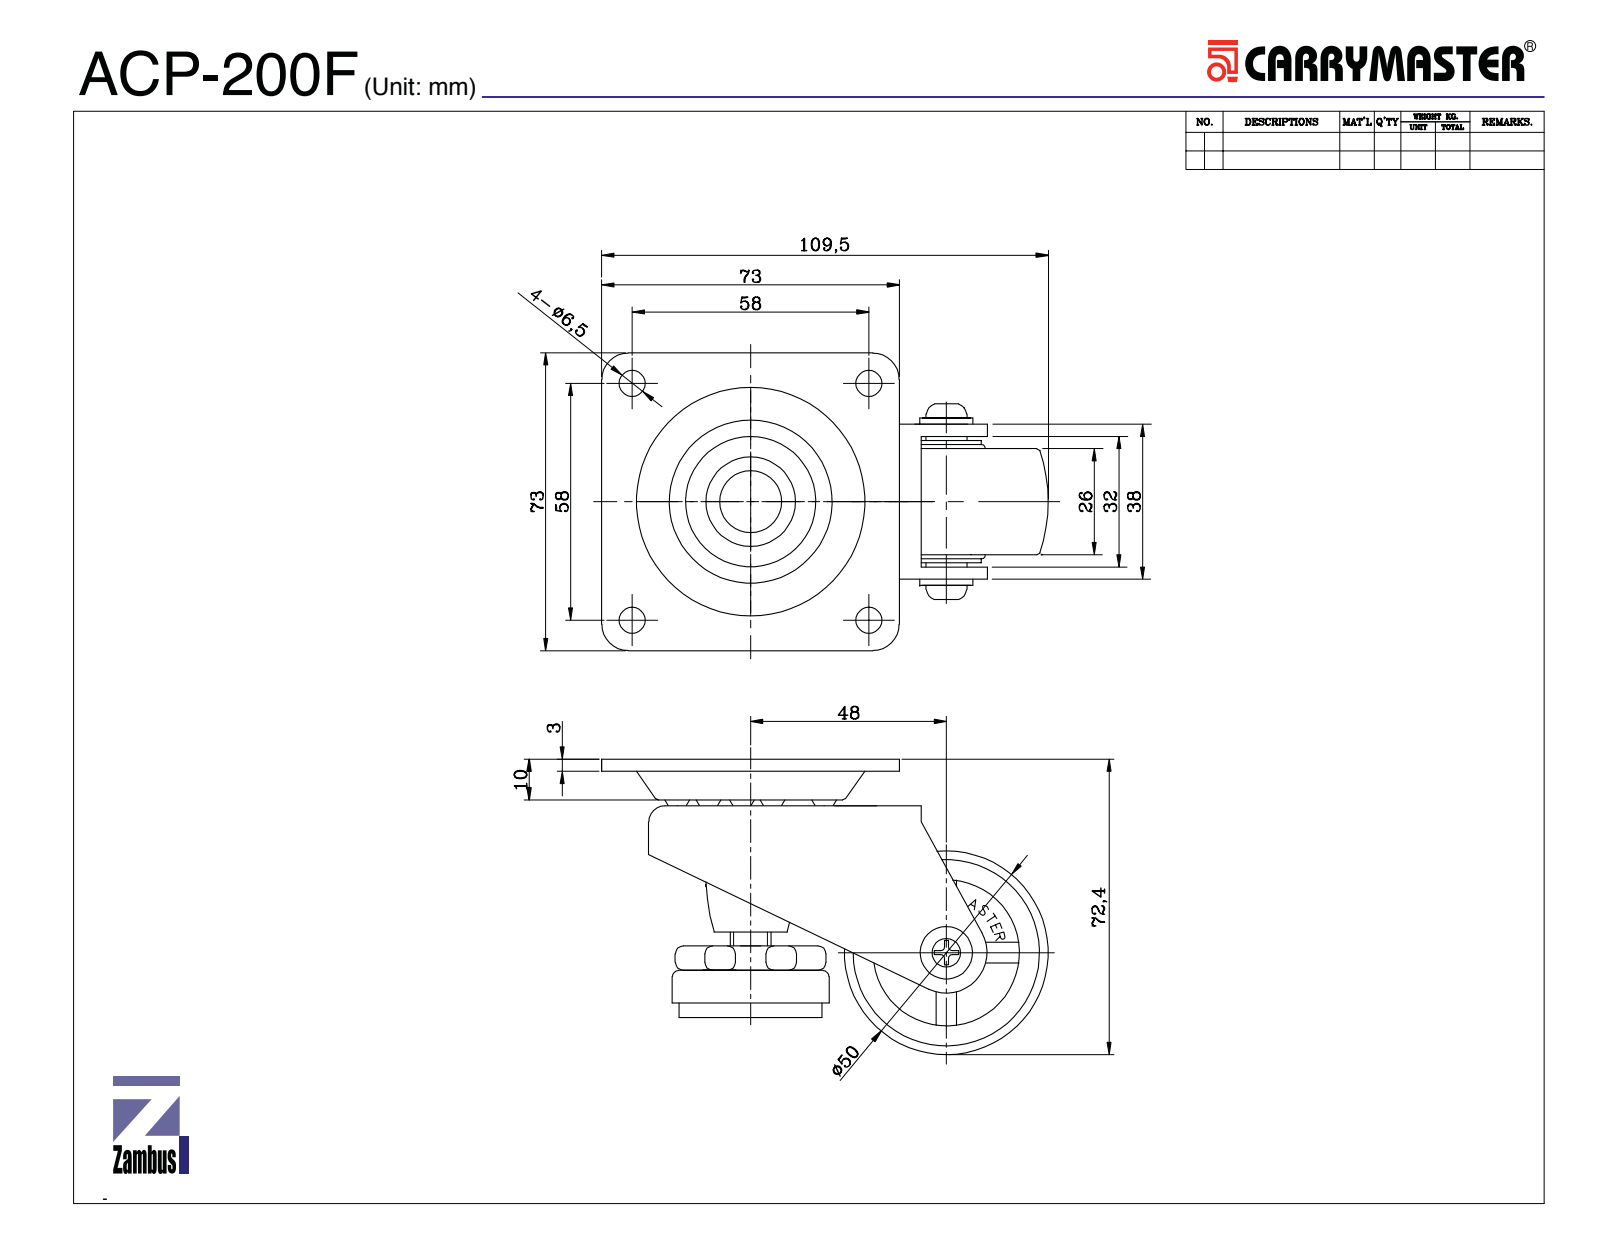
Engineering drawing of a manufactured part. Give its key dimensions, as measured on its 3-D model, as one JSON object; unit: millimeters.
{"part_name": "ACP-200F TOP PLATE; ACP-200F PIN; STEEL BALL-白5; ACP-200F CUP (+8 more)", "step_written_by": "SolidWorks 2015 (CONFIG_CONTROL_DESIGN)", "units": "millimeters", "bodies": {"solids": 48, "faces": 558, "planar": 194, "cylindrical": 117, "other": 247}, "overall_size": [109.5, 73, 72.5], "volume_mm3": 113415, "surface_area_mm2": 60213, "round_holes": [[6.5, 5], [5, 1], [6.8, 1], [8.38, 1], [10.2, 1], [13.5, 1], [14.5, 1], [18, 1], [22, 1], [35.3, 1], [36, 1]], "round_bosses_or_shafts": [[10, 2], [38.5, 1], [37, 1], [35, 1], [25, 1], [20, 1], [19, 1], [17, 1]], "partial_cylinders_radius": [[4, 8], [5, 8], [4.2, 6], [6.5, 4], [100, 2], [104, 2], [10, 1], [20, 1]], "face_to_face_distances": [3, 4, 14.5, 11.5, 47.46, 58.96, 61.96, 45.86, 7.5, 51.46], "hole_center_spacings": [41.01, 58, 82.02]}
